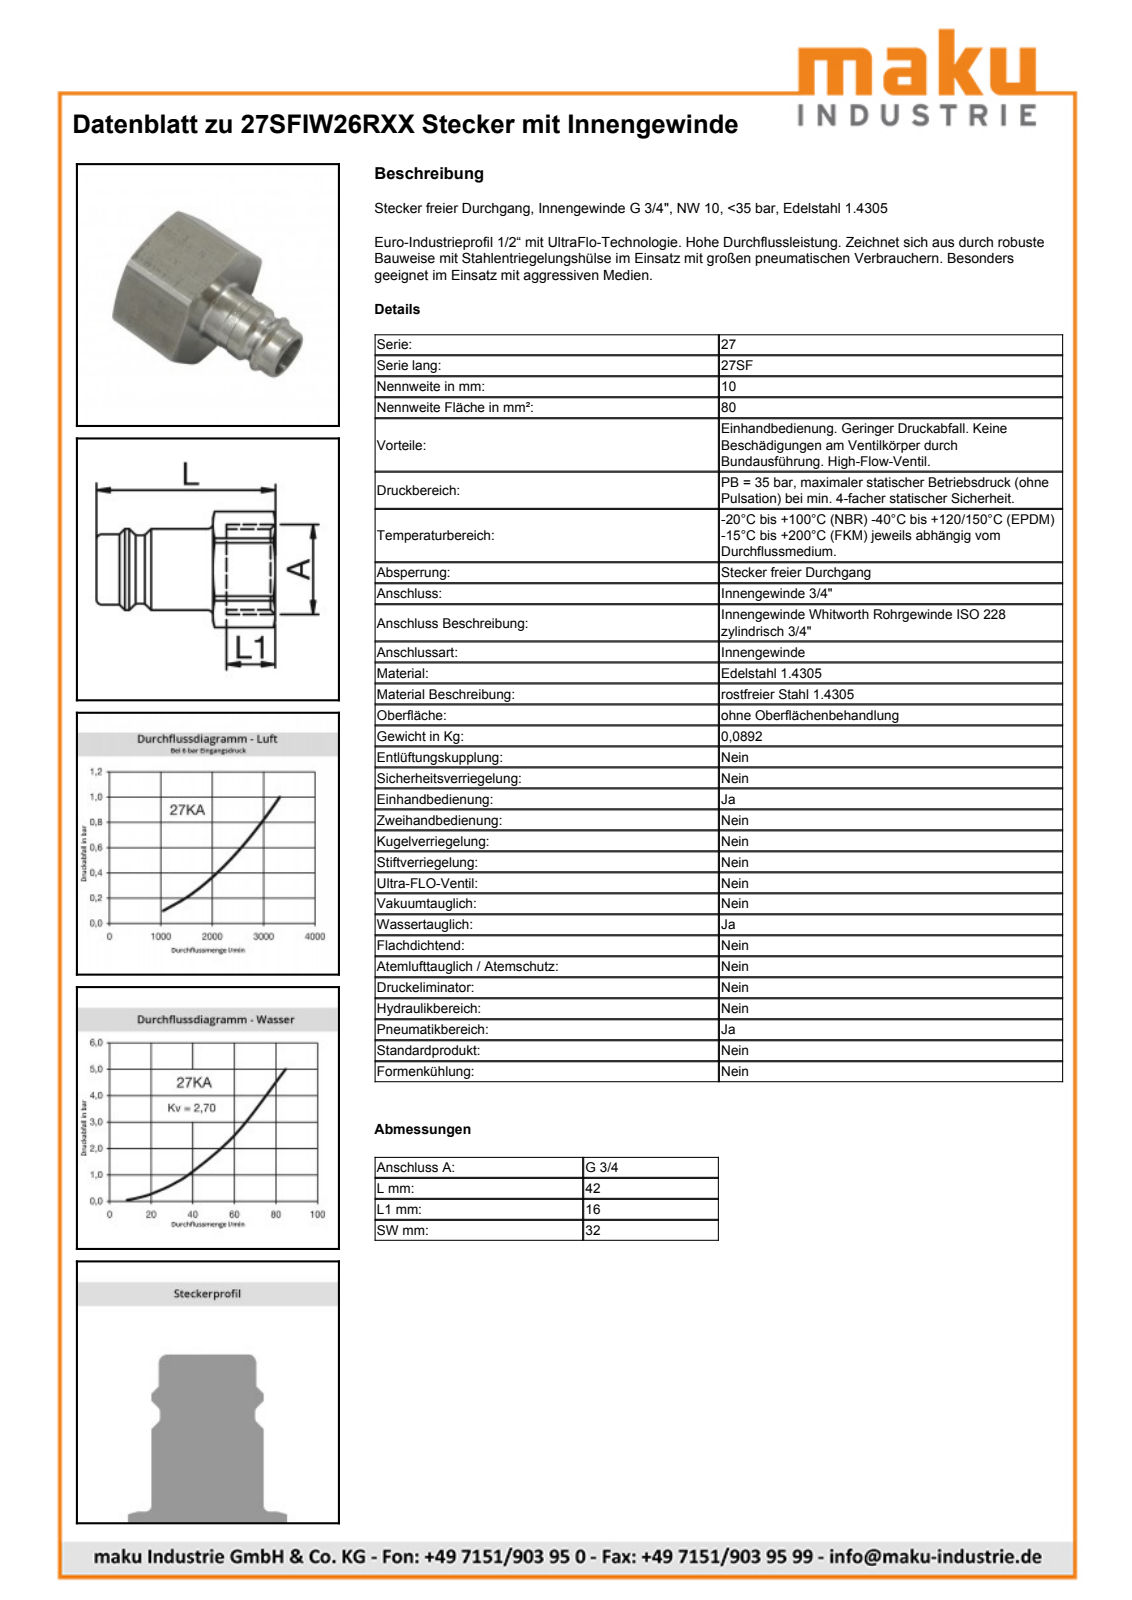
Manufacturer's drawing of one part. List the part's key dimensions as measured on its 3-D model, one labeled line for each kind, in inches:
Part name (STEP PRODUCT): D102306
STEP written by: Autodesk Inventor 2011 (AUTOMOTIVE_DESIGN)
Units: inches
Bodies: 1 solid, 41 faces (10 planar, 11 cylindrical, 20 other)
Overall size (bounding box): 1.657 × 1.382 × 1.26
Volume: 0.863 in³ · Surface area: 9.356 in²
Round holes (diameter × count): ⌀0.95 ×1
Round bosses / shafts (diameter × count): ⌀0.591 ×1, ⌀0.512 ×1, ⌀0.498 ×1
Partial cylindrical surfaces — rounded edges, fillets, slot ends (radius × count): R0.691 ×1
Main face-to-face distances: 1.26, 0.181, 0.811, 0.63, 0.846, 1.028, 1.657
